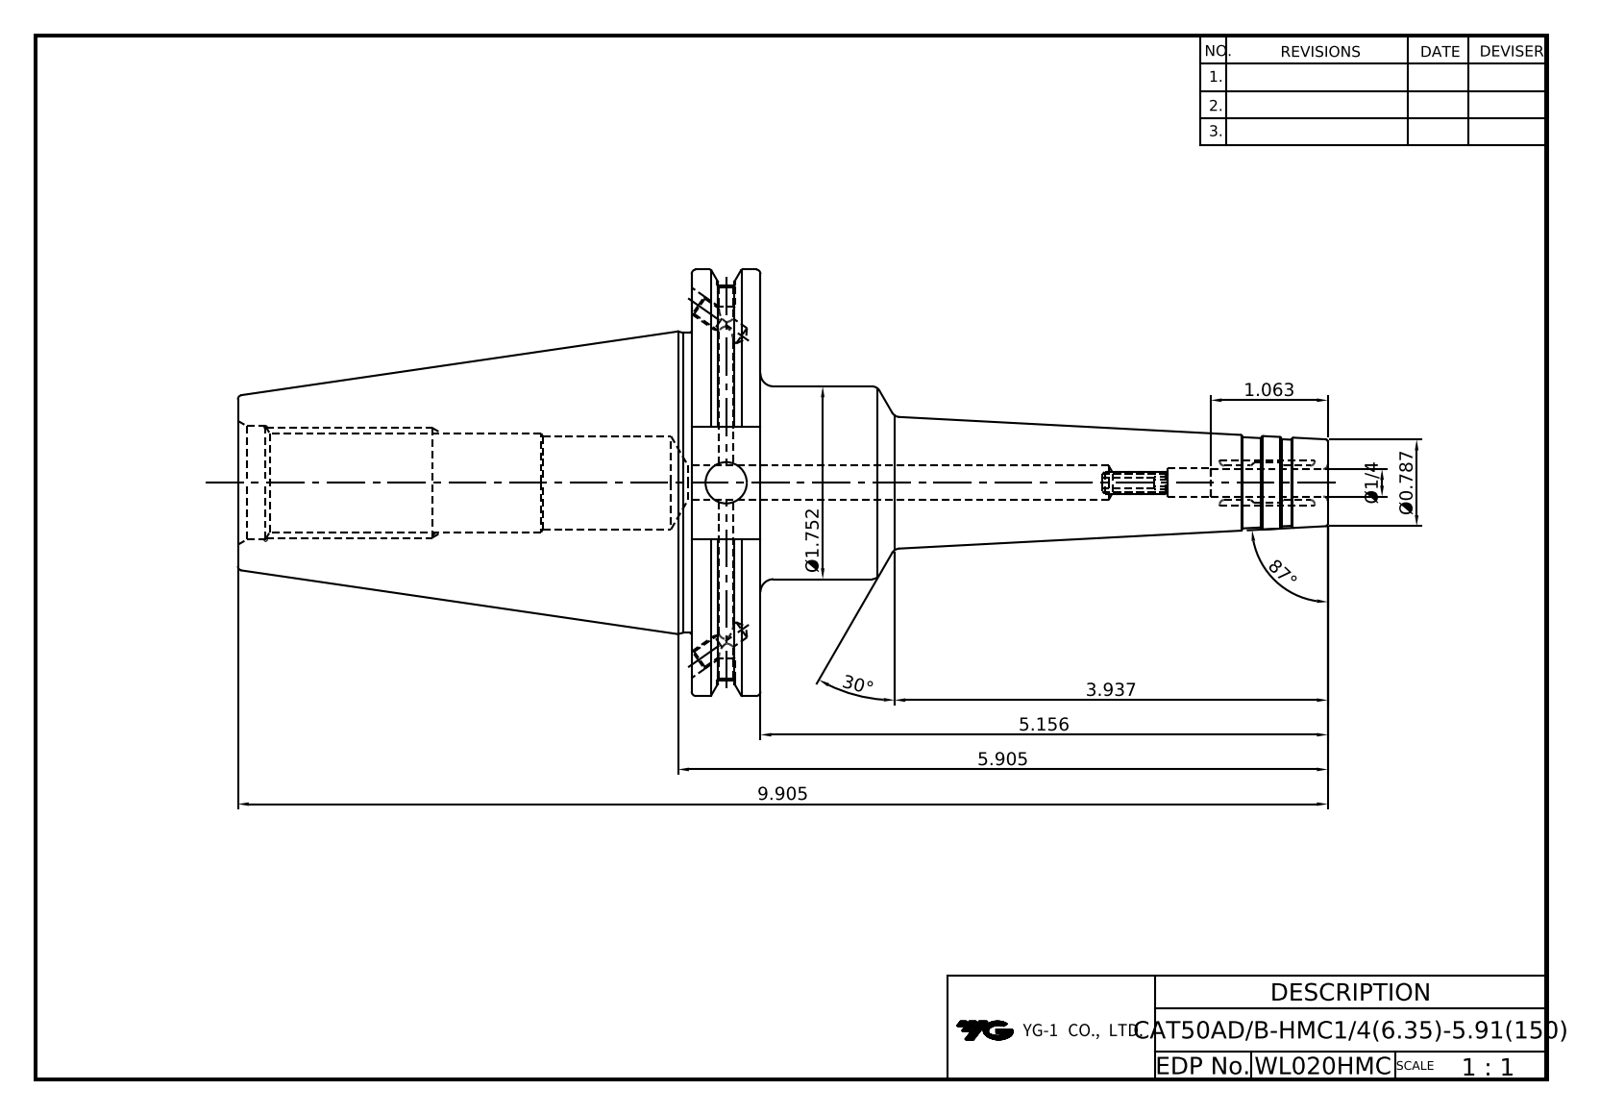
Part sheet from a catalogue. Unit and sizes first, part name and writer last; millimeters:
Units: millimetres
Overall size (bounding box): 251.6 × 98.42 × 94.69
Round holes (diameter × count): ⌀3.24 ×2, ⌀4.13 ×2, ⌀4.2 ×2, ⌀5 ×2, ⌀4.3 ×1, ⌀6.35 ×1, ⌀6.8 ×1, ⌀8 ×1, ⌀9.53 ×1, ⌀21.5 ×1, ⌀21.97 ×1, ⌀26.2 ×1
Round bosses / shafts (diameter × count): ⌀98.42 ×1, ⌀91.29 ×1, ⌀69.25 ×1, ⌀44.5 ×1
Main face-to-face distances: 15.88, 104.77, 120.65, 73.03, 25.9, 251.6, 146.83, 130.95, 110.82, 6.05
Volume: 416 202 mm³ · Surface area: 58 704 mm²
Bodies: 1 solid, 106 faces (37 planar, 28 cylindrical, 41 other)
Part name (STEP PRODUCT): LO-CAT50ADB-HMC6.35-150
STEP written by: Autodesk Inventor 2024 (AUTOMOTIVE_DESIGN)
